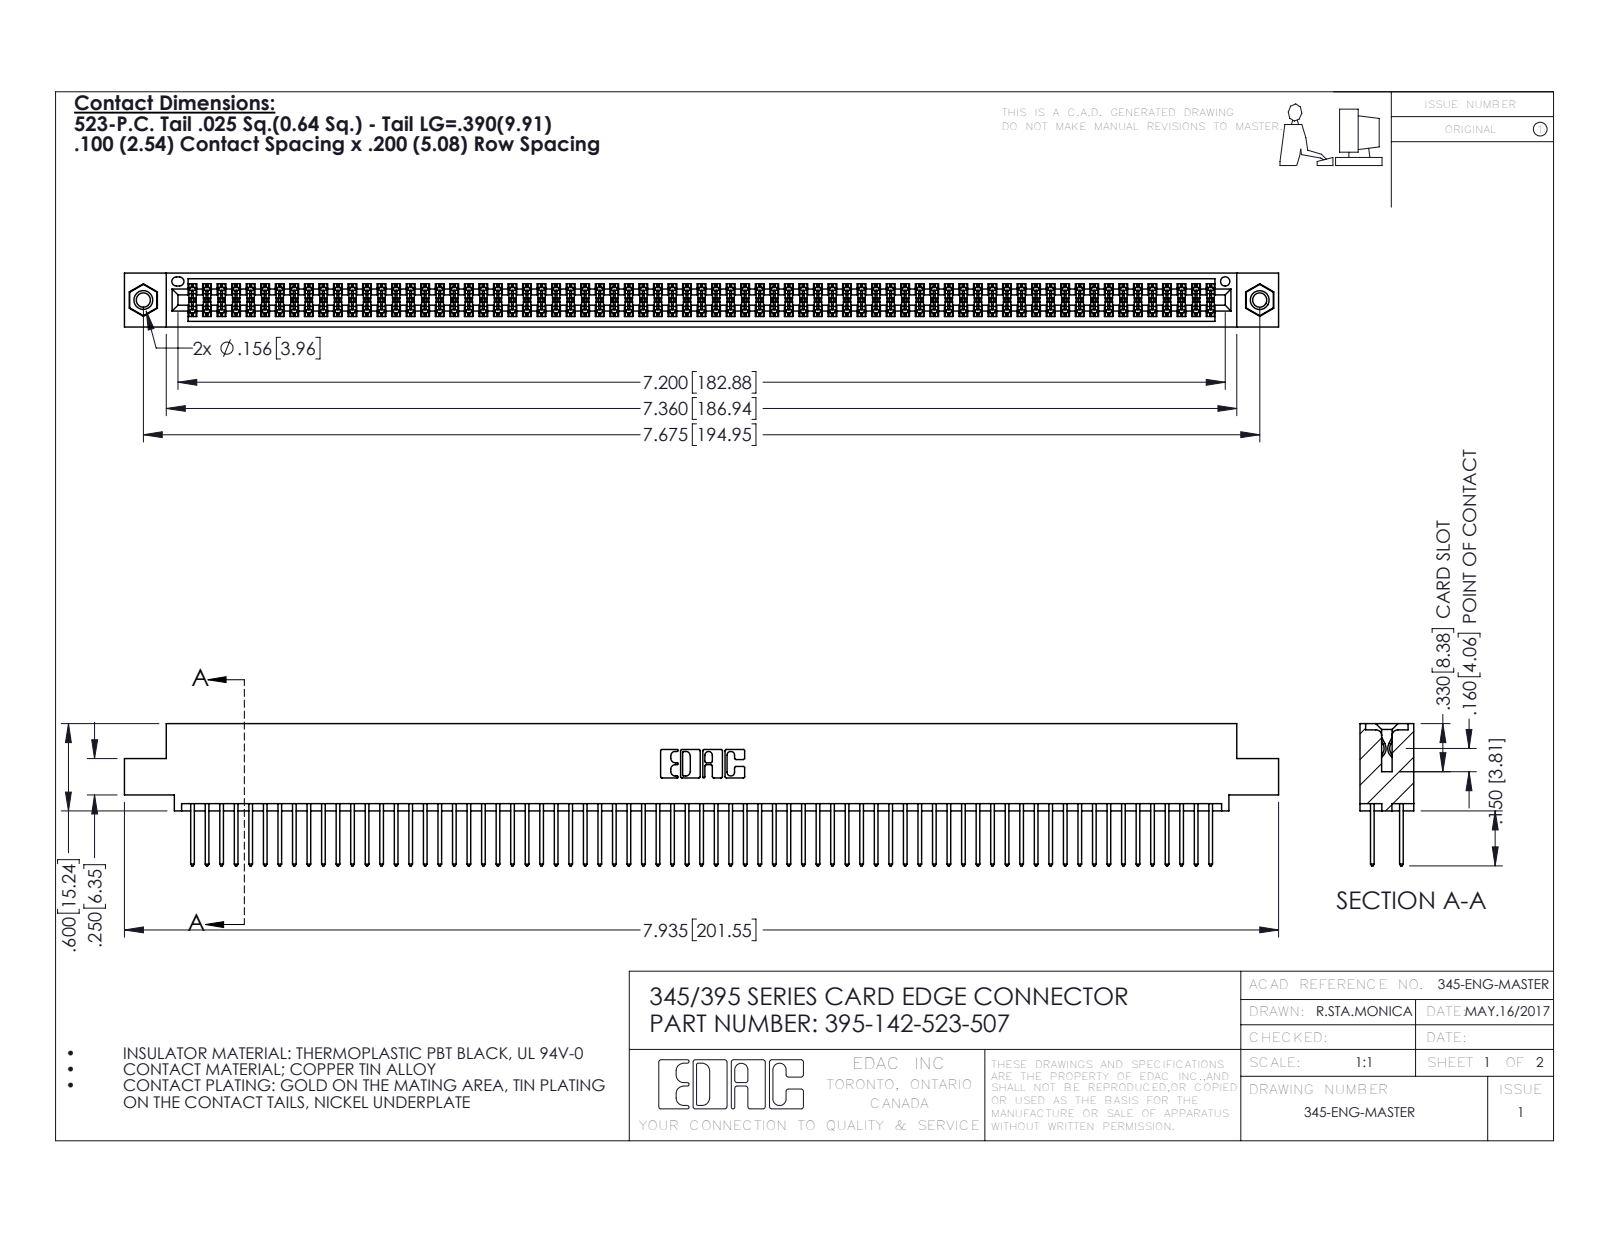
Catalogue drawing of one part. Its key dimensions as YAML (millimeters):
part_name: "345 Part_0.110 Offset - 0.156 Dia-TI; 345-250-001_345-250-005-103; 395-142-523-507; 345-292-001_345-293-123"
step_written_by: "SolidWorks 2016 (CONFIG_CONTROL_DESIGN)"
units: millimeters
bodies: {solids: 145, faces: 7290, planar: 4802, cylindrical: 2472, other: 16}
overall_size: [201.5, 24.8, 9.4]
volume: 20060
surface_area: 31630
round_holes:
  - {diameter: 2.5, count: 2}
  - {diameter: 3.2, count: 2}
  - {diameter: 4, count: 2}
  - {diameter: 1.6, count: 1}
round_bosses_or_shafts:
  - {diameter: 3.9, count: 2}
partial_cylinders:
  - {radius: 0.2, count: 213}
  - {radius: 0.3, count: 142}
  - {radius: 0.3, count: 22}
  - {radius: 0.2, count: 6}
  - {radius: 0.8, count: 6}
  - {radius: 0.7, count: 3}
  - {radius: 0.4, count: 2}
  - {radius: 0.5, count: 2}
face_to_face_distances: [1.8, 7.6, 5.1, 2.5, 6.9, 0.6, 9.4, 5.7, 4.4, 3.8]
hole_center_spacings: [6.9, 189, 194.9]
